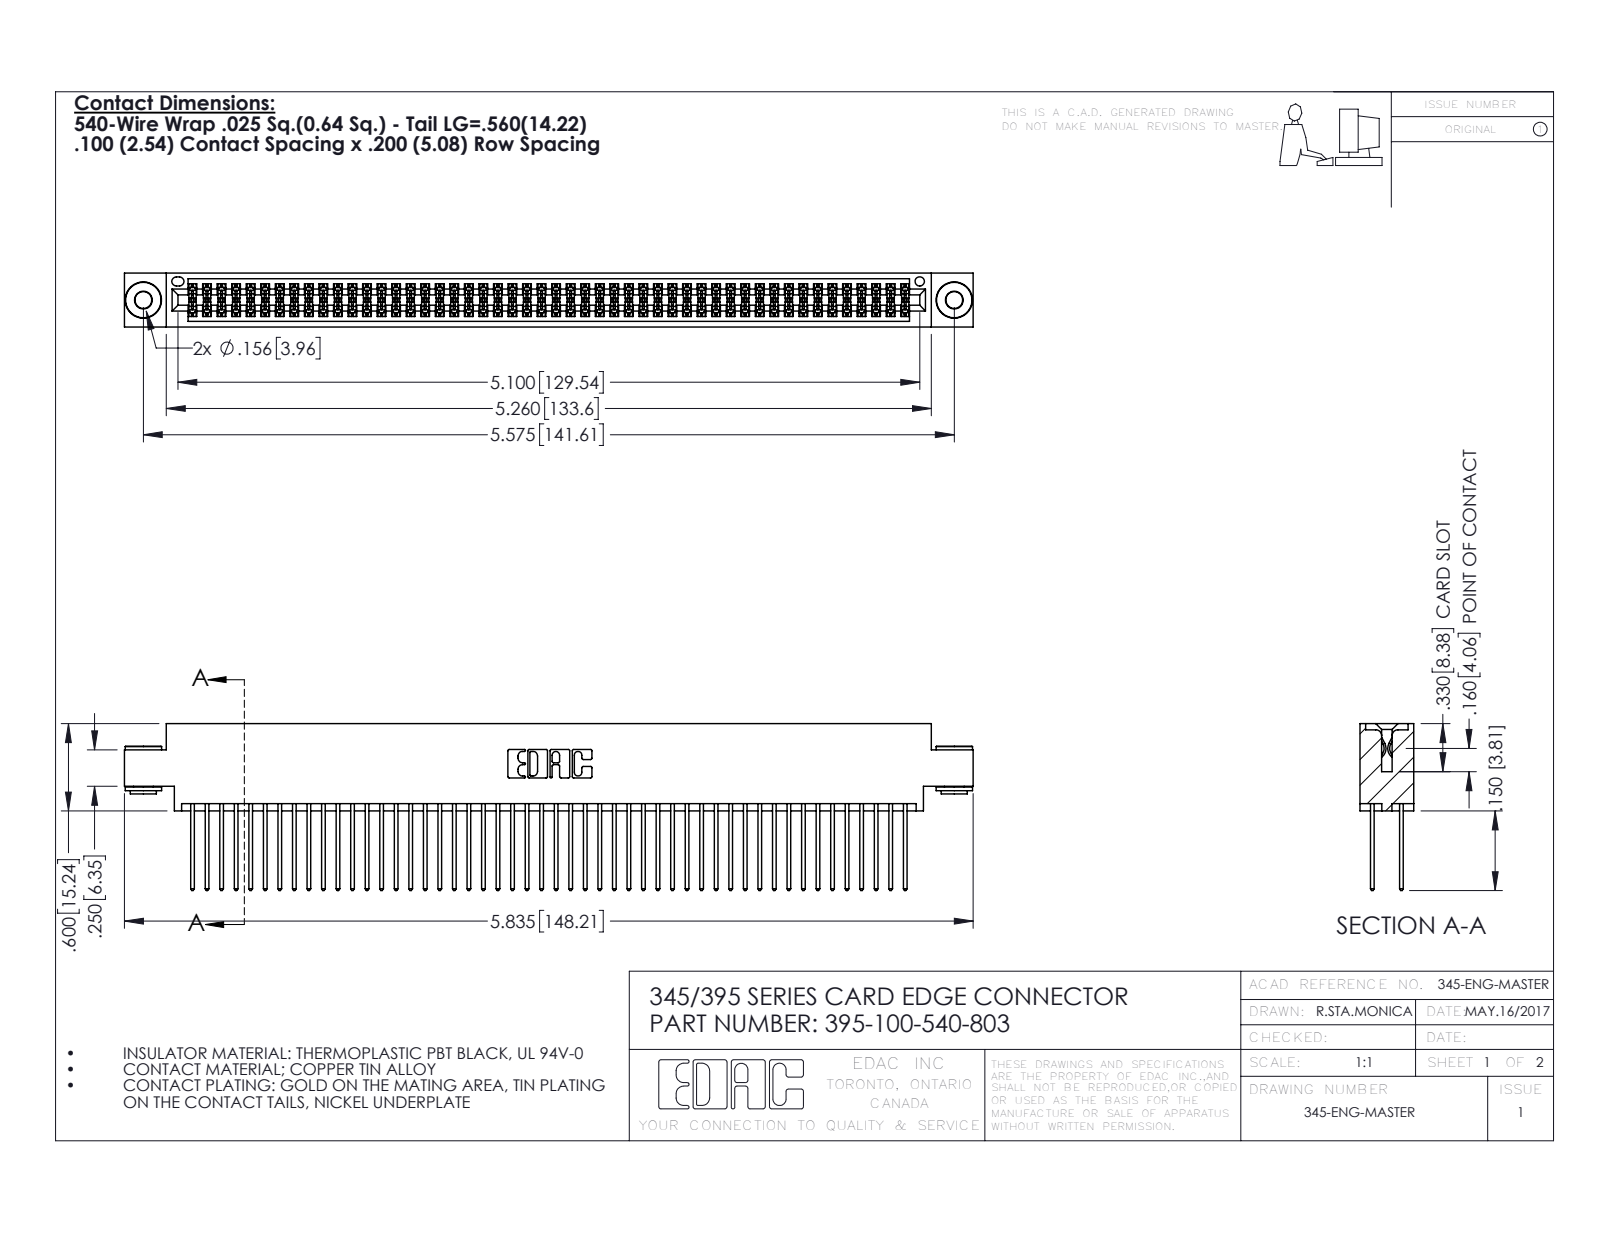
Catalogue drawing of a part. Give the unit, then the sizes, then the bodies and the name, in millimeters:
Units: millimetres
Overall size (bounding box): 148.2 × 29.1 × 9.4
Round holes (diameter × count): ⌀2.9 ×2, ⌀4 ×2, ⌀1.6 ×1
Round bosses / shafts (diameter × count): ⌀6.4 ×2, ⌀4.6 ×2, ⌀3.5 ×2
Partial cylindrical surfaces — rounded edges, fillets, slot ends (radius × count): R0.2 ×150, R0.3 ×100, R0.3 ×22, R0.2 ×6, R0.8 ×6, R0.7 ×3, R0.4 ×2, R0.5 ×2
Main face-to-face distances: 1.8, 7.6, 5.1, 2.5, 6.9, 0.6, 9.4, 5.7, 4.4, 3.8
Hole centre spacings: 6.9, 135.6, 141.6
Volume: 14 700 mm³ · Surface area: 24 080 mm²
Bodies: 103 solids, 5168 faces (3394 planar, 1766 cylindrical, 8 other)
Part name (STEP PRODUCT): 345-292-001_345-293-140; 345-250-002_345-250-002-102; 345 Part_0.170 Offset - 0.156 Dia-TH; 395-100-540-803
STEP written by: SolidWorks 2016 (CONFIG_CONTROL_DESIGN)
